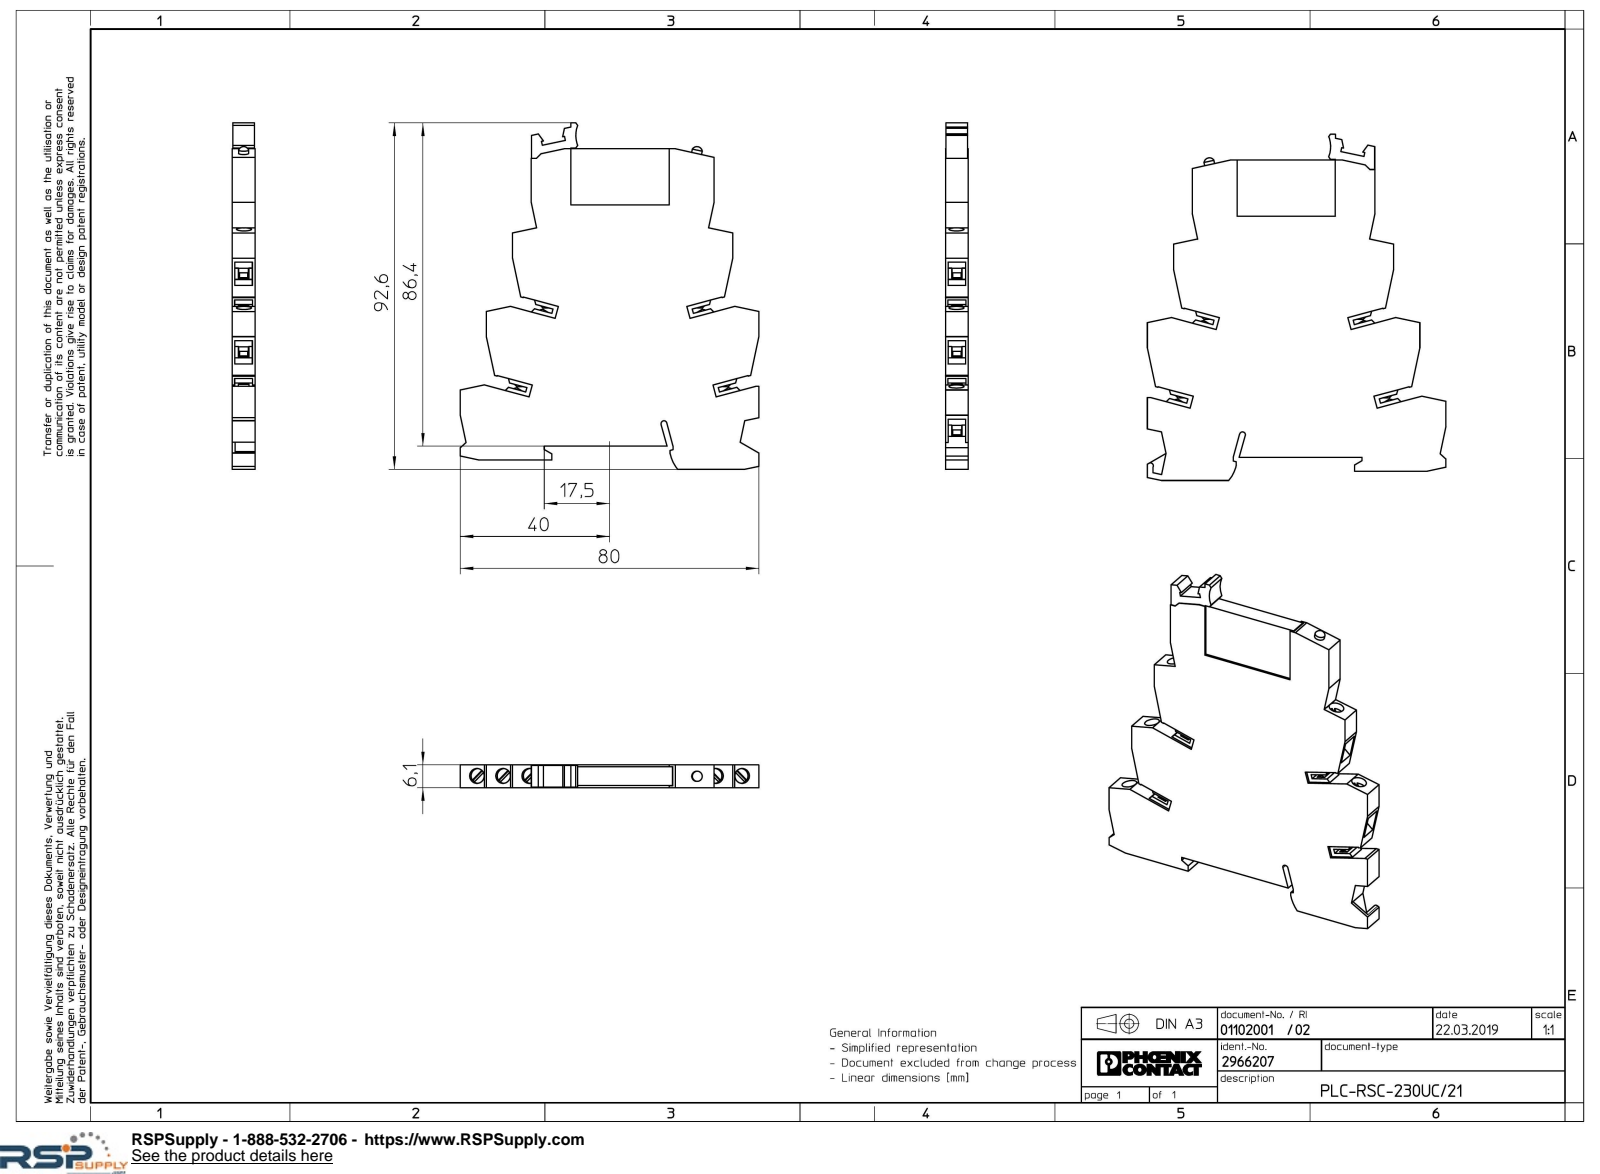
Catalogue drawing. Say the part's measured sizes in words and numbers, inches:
The part is named "PLC-BSC-6-ACT-SOC05-select; REL-MR-28x15x5-select; PLC-RSC-6-REL_WH-Group-select". Its 3-D file was written by "Creo Elements/Direct Modeling 20.1A 29-Sep-2018 (C) Parametric Technology GmbH (AUTOMOTIVE_DESIGN)". It is 2 solids with 367 faces: 348 planar, 5 cylindrical and 14 other. Overall it measures 3.646 by 3.15 by 0.24 inches. Its volume is 1.837 cubic inches and its surface area 22.76 square inches. Partial cylindrical surfaces (rounded edges, fillets, slot ends): 2 of radius 0.031, 1 of radius 0.03, 1 of radius 0.276, 1 of radius 0.374. The main face-to-face distances are 0.24, 0.022, 0.219, 0.197, 0.041, 0.146, 0.213, 0.047, 2.539, 0.15.
